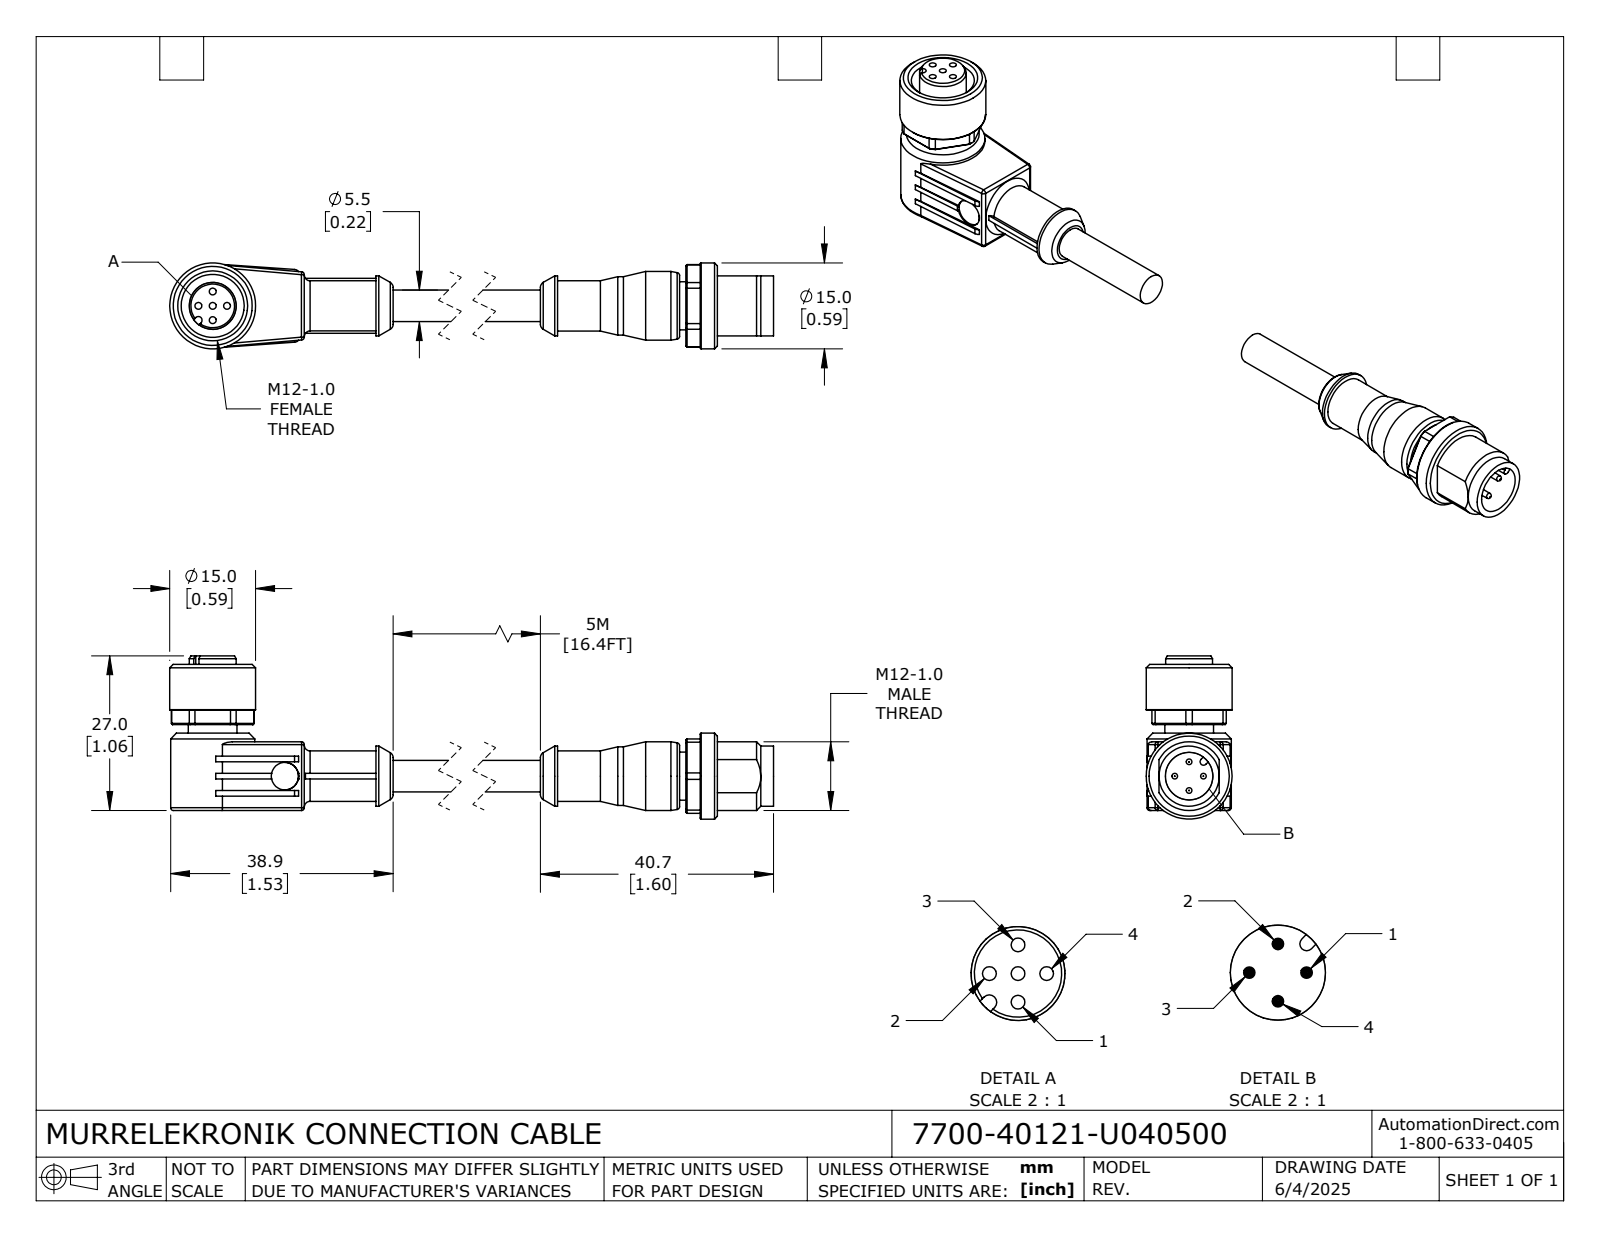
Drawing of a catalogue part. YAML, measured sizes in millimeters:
part_name: "7700-40121-U040500; 7700-40121-U040500_FEMALE; 7700-40121-U040500_MALE"
step_written_by: "SolidWorks 2024 (CONFIG_CONTROL_DESIGN)"
units: millimeters
bodies: {solids: 2, faces: 248, planar: 91, cylindrical: 95, other: 62}
overall_size: [144.7, 28.5, 15]
volume: 10768
surface_area: 6089
round_holes:
  - {diameter: 1.2, count: 5}
  - {diameter: 4.8, count: 1}
  - {diameter: 8.3, count: 1}
  - {diameter: 11, count: 1}
round_bosses_or_shafts:
  - {diameter: 1, count: 4}
  - {diameter: 15, count: 2}
  - {diameter: 14.7, count: 1}
  - {diameter: 12, count: 1}
  - {diameter: 10.5, count: 1}
  - {diameter: 10.2, count: 1}
  - {diameter: 8.8, count: 1}
  - {diameter: 8.5, count: 1}
partial_cylinders:
  - {radius: 0.5, count: 8}
  - {radius: 1, count: 2}
  - {radius: 7.2, count: 2}
  - {radius: 0.6, count: 1}
  - {radius: 0.65, count: 1}
face_to_face_distances: [3, 12, 1.5, 13.5, 5.5, 15, 13, 6, 10.5, 2.5]
hole_center_spacings: [2.5, 3.54, 5]
